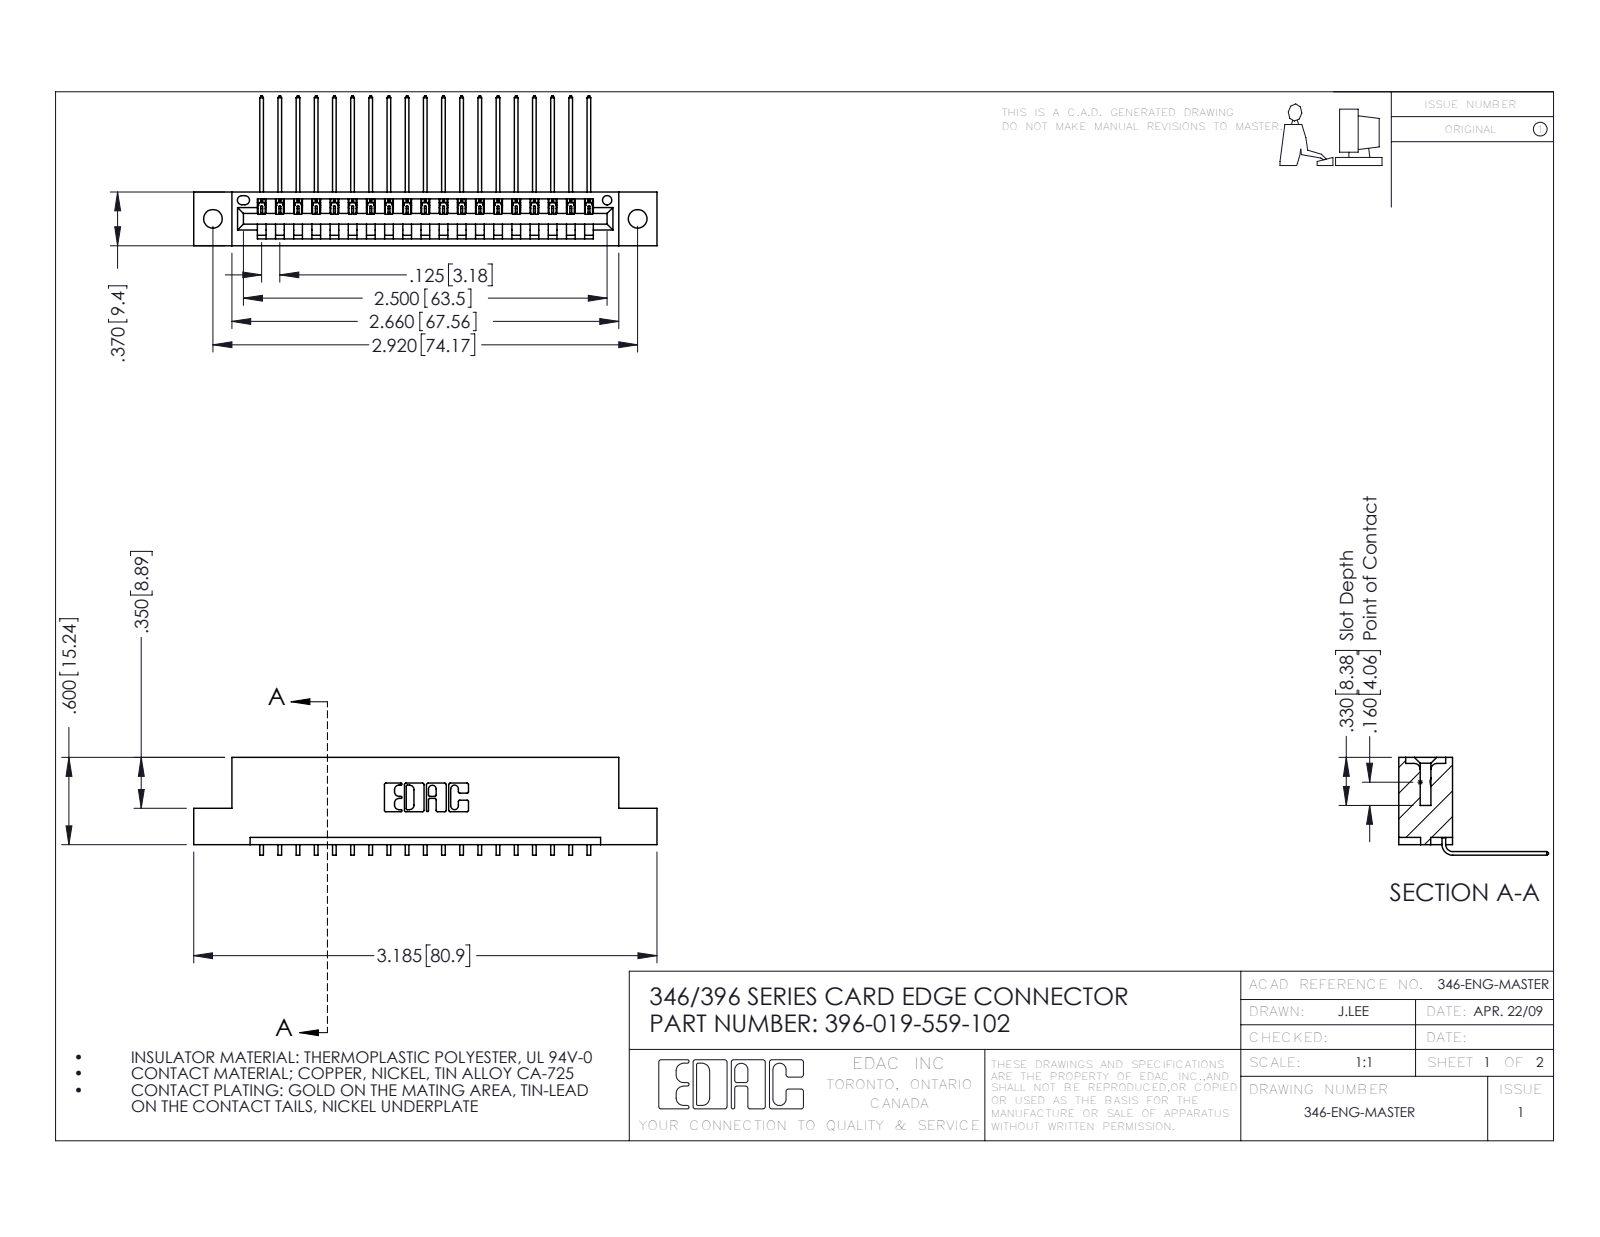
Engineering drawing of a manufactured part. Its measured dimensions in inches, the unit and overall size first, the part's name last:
Units: inches
Overall size (bounding box): 3.185 × 1.03 × 0.673
Round holes (diameter × count): ⌀0.128 ×2, ⌀0.064 ×1
Partial cylindrical surfaces — rounded edges, fillets, slot ends (radius × count): R0.006 ×38, R0.01 ×22, R0.007 ×6, R0.031 ×6, R0.026 ×3, R0.031 ×2, R0.04 ×2, R0.014 ×1
Main face-to-face distances: 0.048, 0.322, 0.37, 0.25, 0.072, 0.025, 0.298, 0.148, 0.222, 0.1
Hole centre spacings: 0.246, 2.713, 2.92
Volume: 0.465 in³ · Surface area: 14.53 in²
Bodies: 20 solids, 1262 faces (874 planar, 388 cylindrical, 0 other)
Part name (STEP PRODUCT): 345-292-001_558 559 Tail - 1; 346 Part_Flush Mounting Lugs - 0.128 Dia; 396-019-559-102
STEP written by: SolidWorks 2016 (CONFIG_CONTROL_DESIGN)
